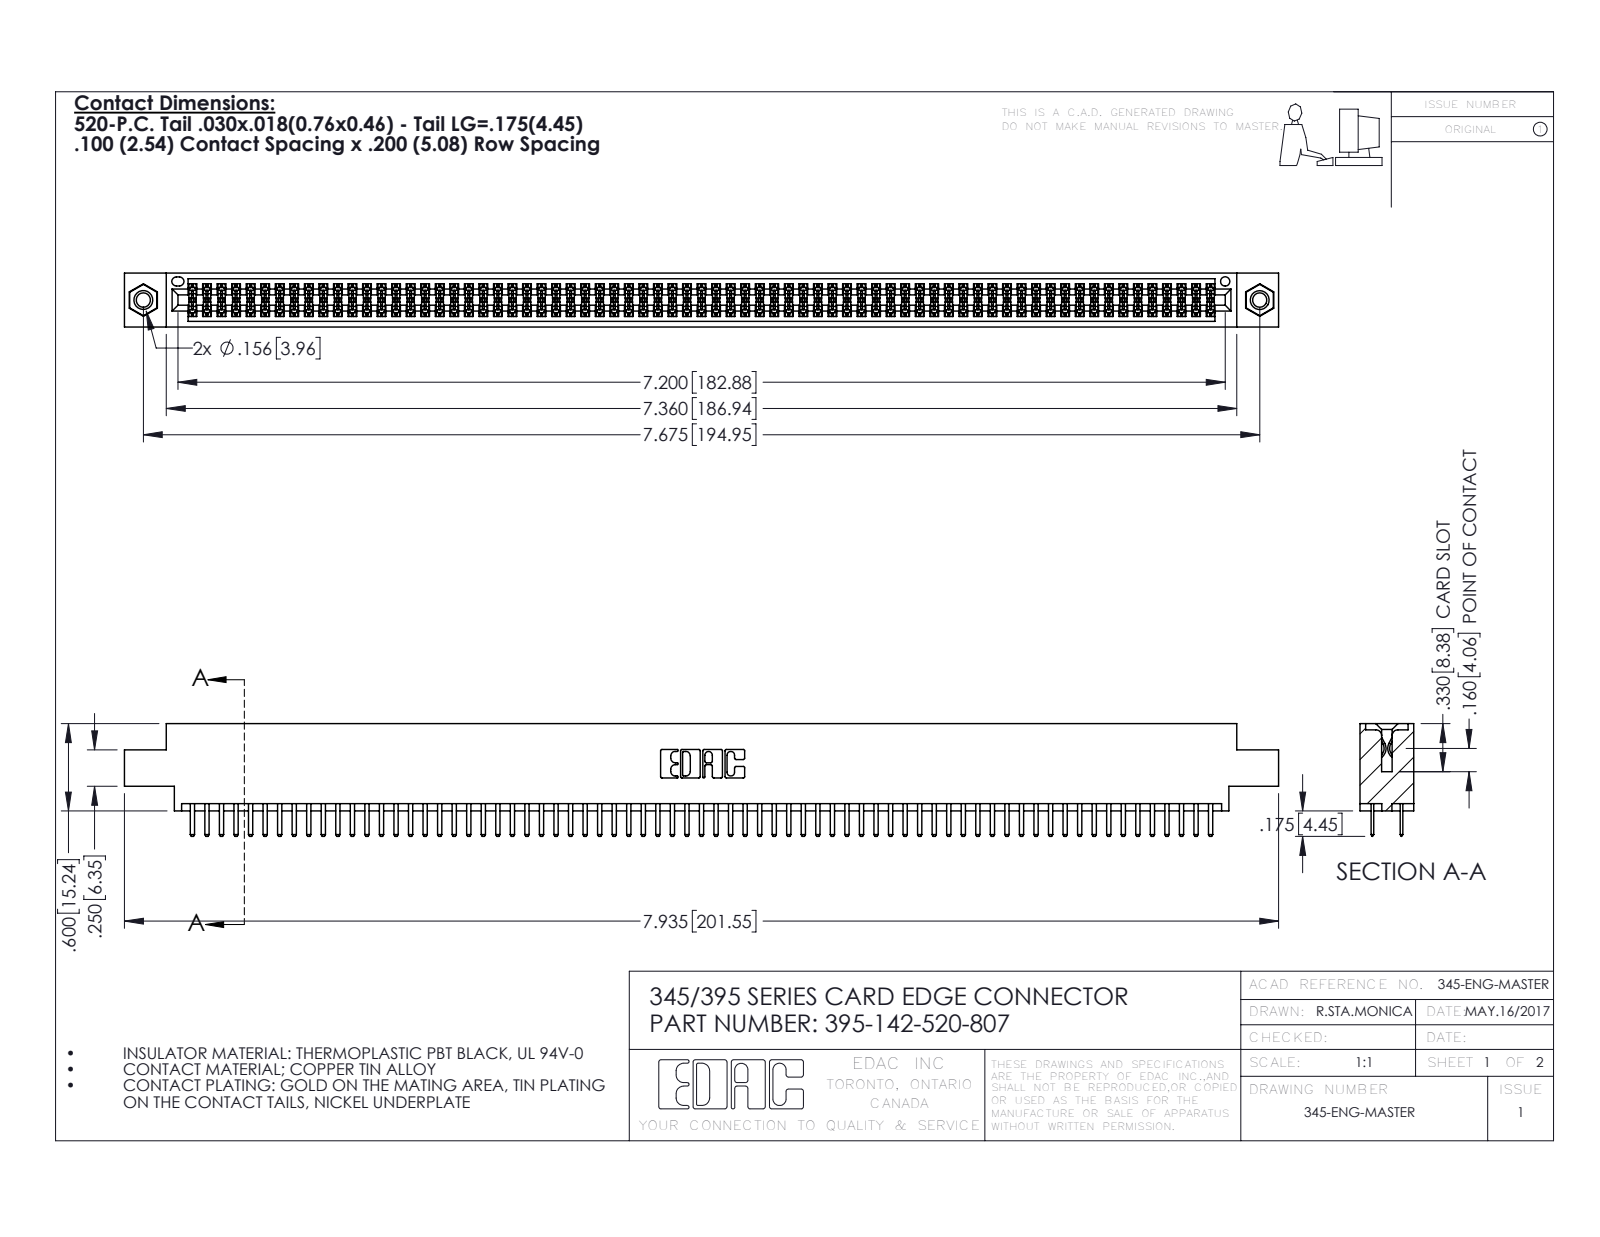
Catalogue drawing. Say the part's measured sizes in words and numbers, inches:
The part is named "345-292-001_345-293-120; 395-142-520-807; 345-250-001_345-250-005-103; 345 Part_0.170 Offset - 0.156 Dia-TI". Its 3-D file was written by "SolidWorks 2016 (CONFIG_CONTROL_DESIGN)". It is 145 solids with 7858 faces: 5086 planar, 2756 cylindrical and 16 other. Overall it measures 7.935 by 0.775 by 0.37 inches. Its volume is 1.2 cubic inches and its surface area 45.97 square inches. Round holes: 2 of diameter 0.098, 2 of diameter 0.125, 2 of diameter 0.156, 1 of diameter 0.064. Round bosses or shafts: 2 of diameter 0.155. Partial cylindrical surfaces (rounded edges, fillets, slot ends): 213 of radius 0.006, 146 of radius 0.01, 22 of radius 0.01, 6 of radius 0.007, 6 of radius 0.031, 3 of radius 0.026, 2 of radius 0.014, 2 of radius 0.019. The main face-to-face distances are 0.072, 0.298, 0.2, 0.37, 0.098, 0.272, 0.025, 0.225, 0.022, 0.072. The hole center spacings are 0.27, 7.439, 7.675.
